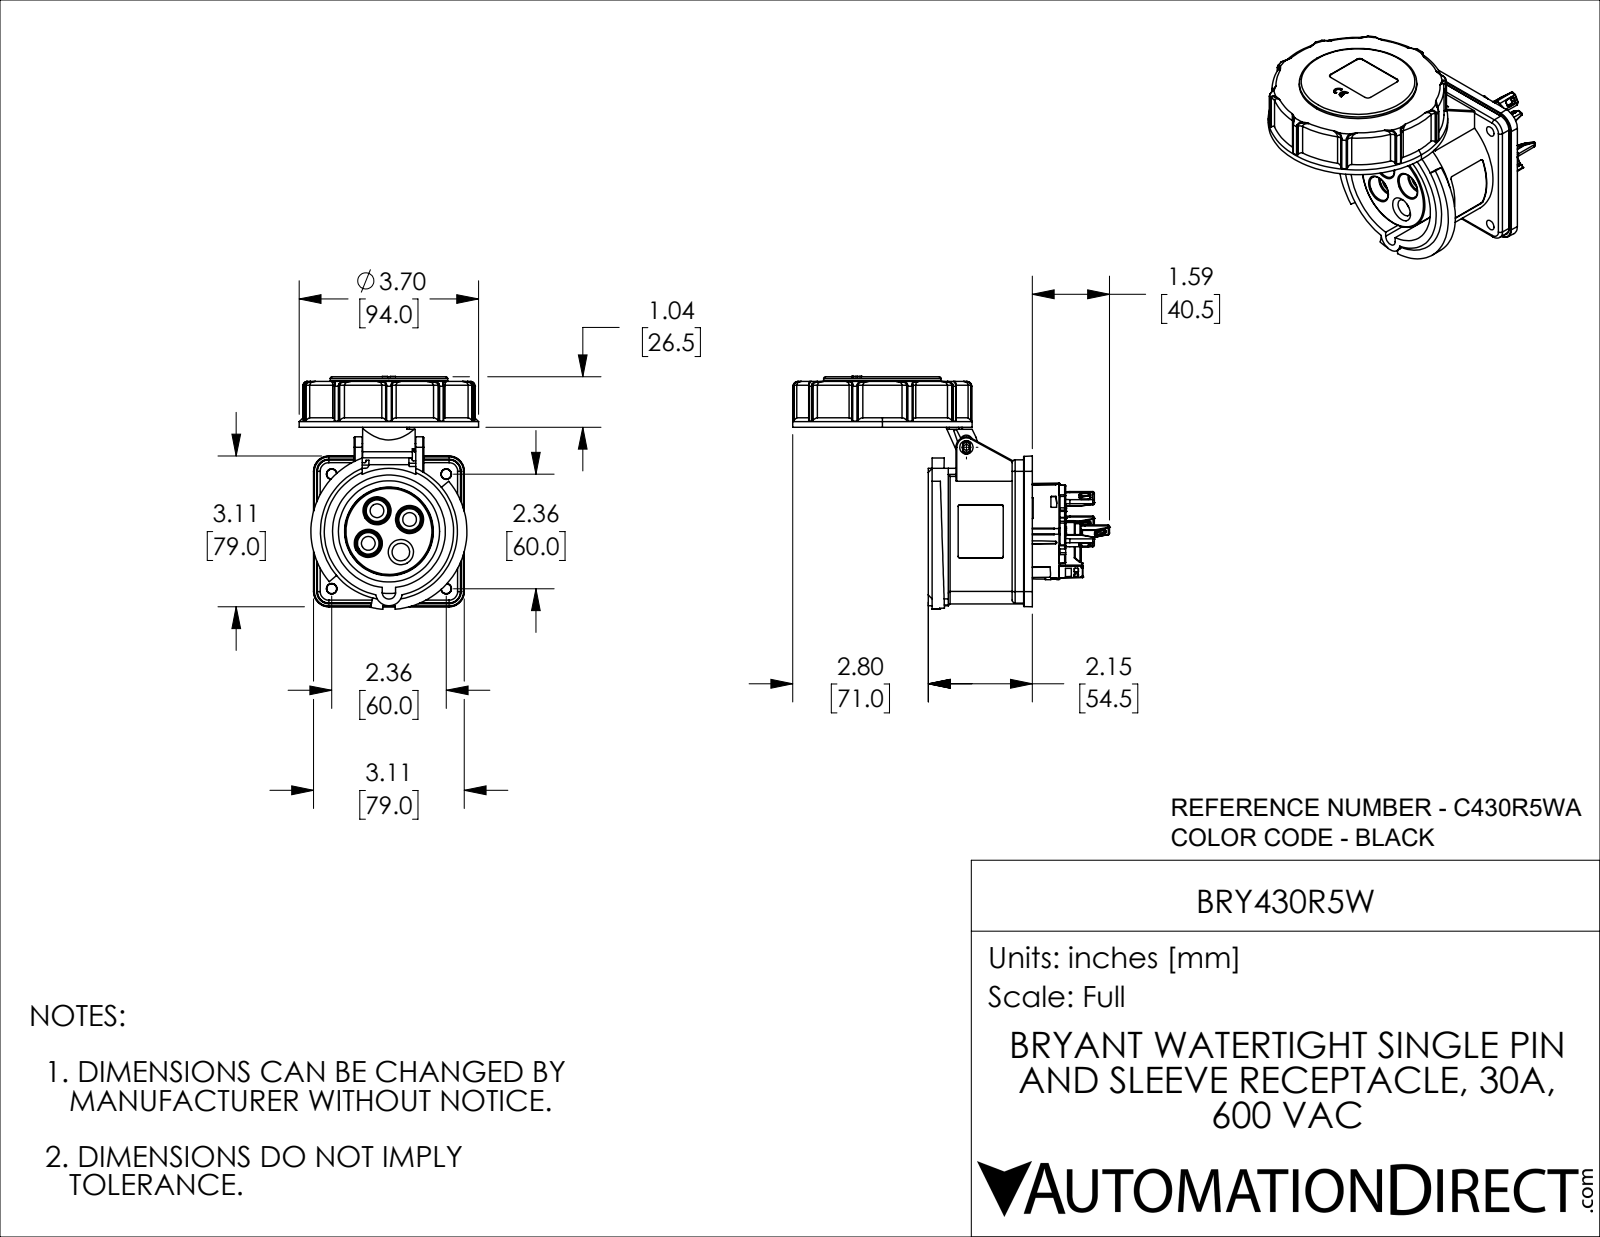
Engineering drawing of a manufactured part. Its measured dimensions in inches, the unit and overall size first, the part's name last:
Units: inches
Overall size (bounding box): 6.535 × 4.801 × 3.701
Round holes (diameter × count): ⌀0.165 ×4, ⌀0.217 ×4, ⌀0.283 ×3, ⌀0.118 ×1, ⌀0.169 ×1, ⌀0.276 ×1, ⌀0.362 ×1, ⌀2.087 ×1, ⌀2.327 ×1, ⌀2.559 ×1, ⌀3.307 ×1
Round bosses / shafts (diameter × count): ⌀3.701 ×1, ⌀2.825 ×1, ⌀2.52 ×1, ⌀2.421 ×1, ⌀2.343 ×1, ⌀0.157 ×1
Partial cylindrical surfaces — rounded edges, fillets, slot ends (radius × count): R0.02 ×93, R0.01 ×85, R0.039 ×28, R0.098 ×27, R0.031 ×24, R0.008 ×12, R0.012 ×9, R0.019 ×8
Main face-to-face distances: 0.925, 0.098, 0.827, 0.413, 0.118, 0.079, 2.067, 1.043, 1.654, 0.945
Hole centre spacings: 0.492, 0.696, 0.979, 1.202, 1.615, 1.67, 1.86, 2.15
Volume: 21.12 in³ · Surface area: 128.7 in²
Bodies: 2 solids, 2055 faces (578 planar, 800 cylindrical, 677 other)
Part name (STEP PRODUCT): BRY430R5W
STEP written by: SolidWorks 2021 (CONFIG_CONTROL_DESIGN)
